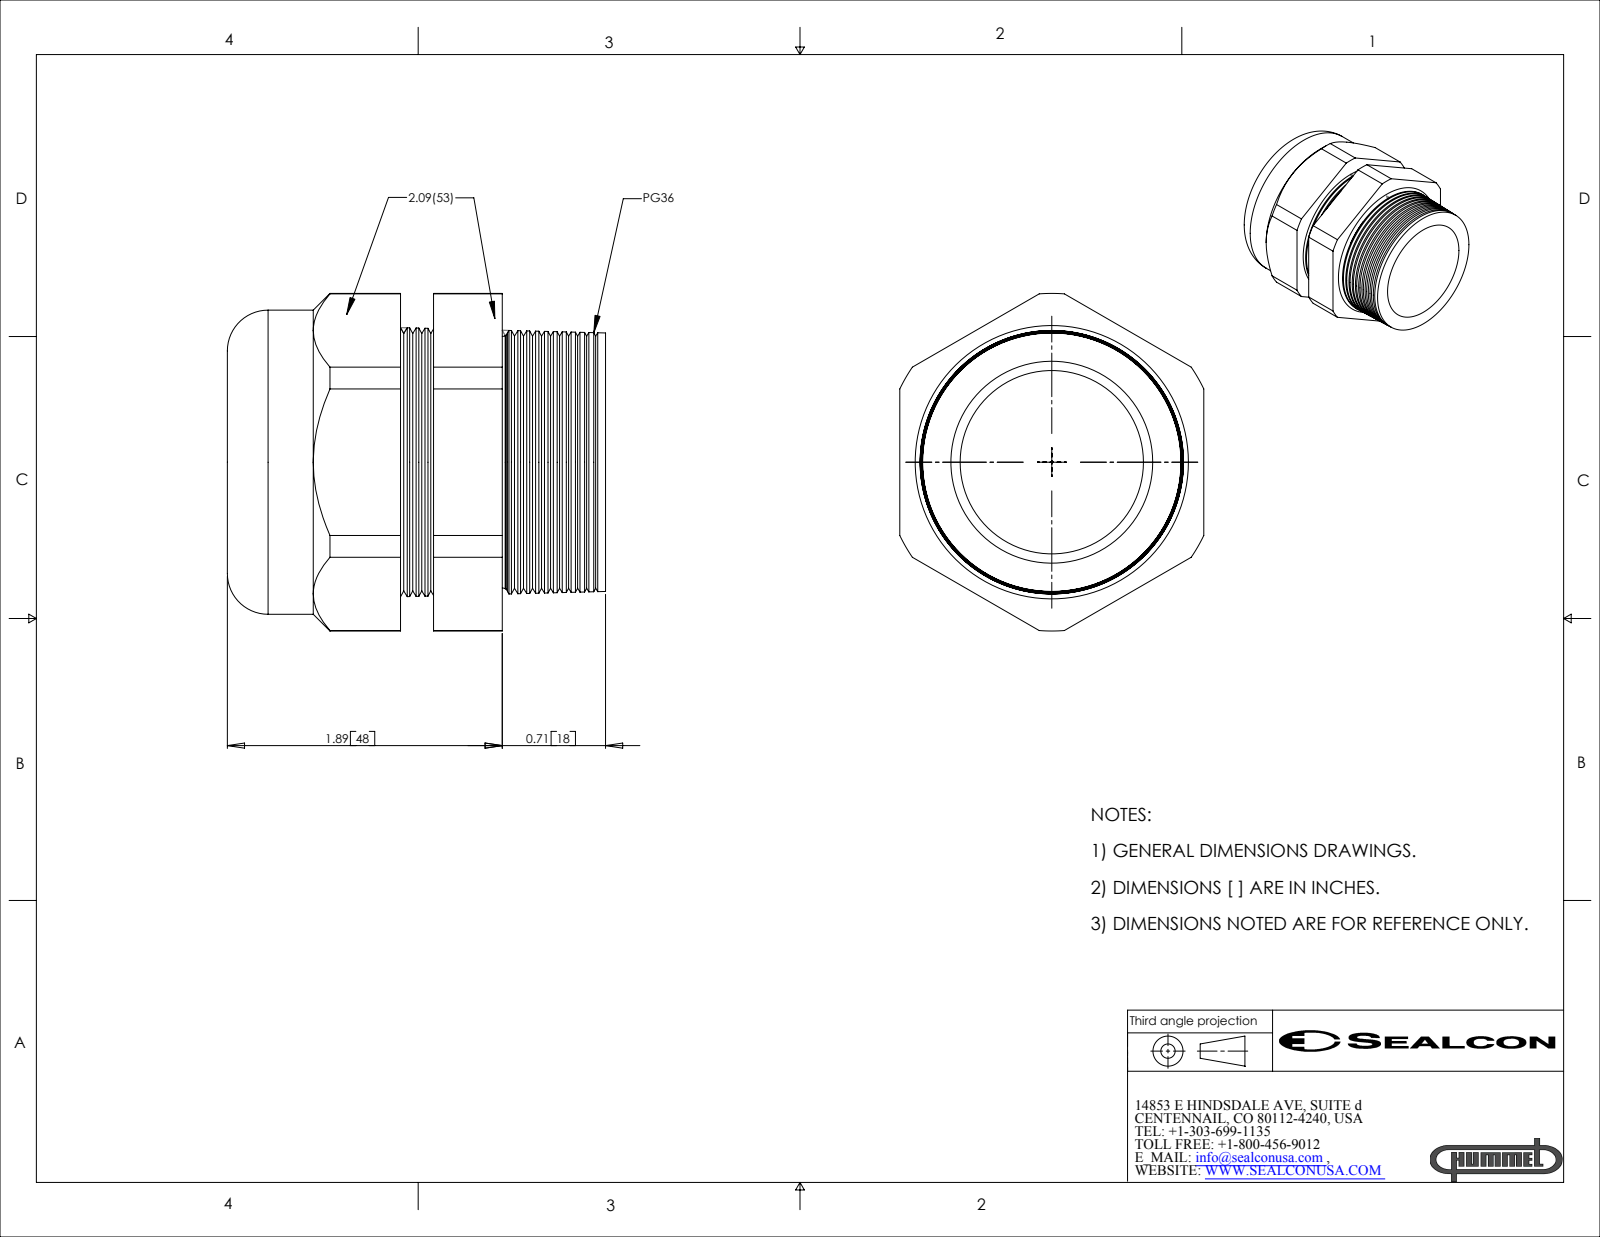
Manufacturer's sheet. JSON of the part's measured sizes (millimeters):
{"part_name": "CD36CA-GY", "step_written_by": "SolidWorks 2007 (CONFIG_CONTROL_DESIGN)", "units": "millimeters", "bodies": {"solids": 2, "faces": 152, "planar": 20, "cylindrical": 22, "other": 110}, "overall_size": [66, 58.9, 53.1], "volume_mm3": 79280, "surface_area_mm2": 27180, "round_holes": [[32, 1], [35.2, 1]], "round_bosses_or_shafts": [[53.1, 1]], "partial_cylinders_radius": [[29.5, 1]], "face_to_face_distances": [53.1, 5.8, 17.8, 12, 35.8, 30, 18, 15.2, 21, 33]}
